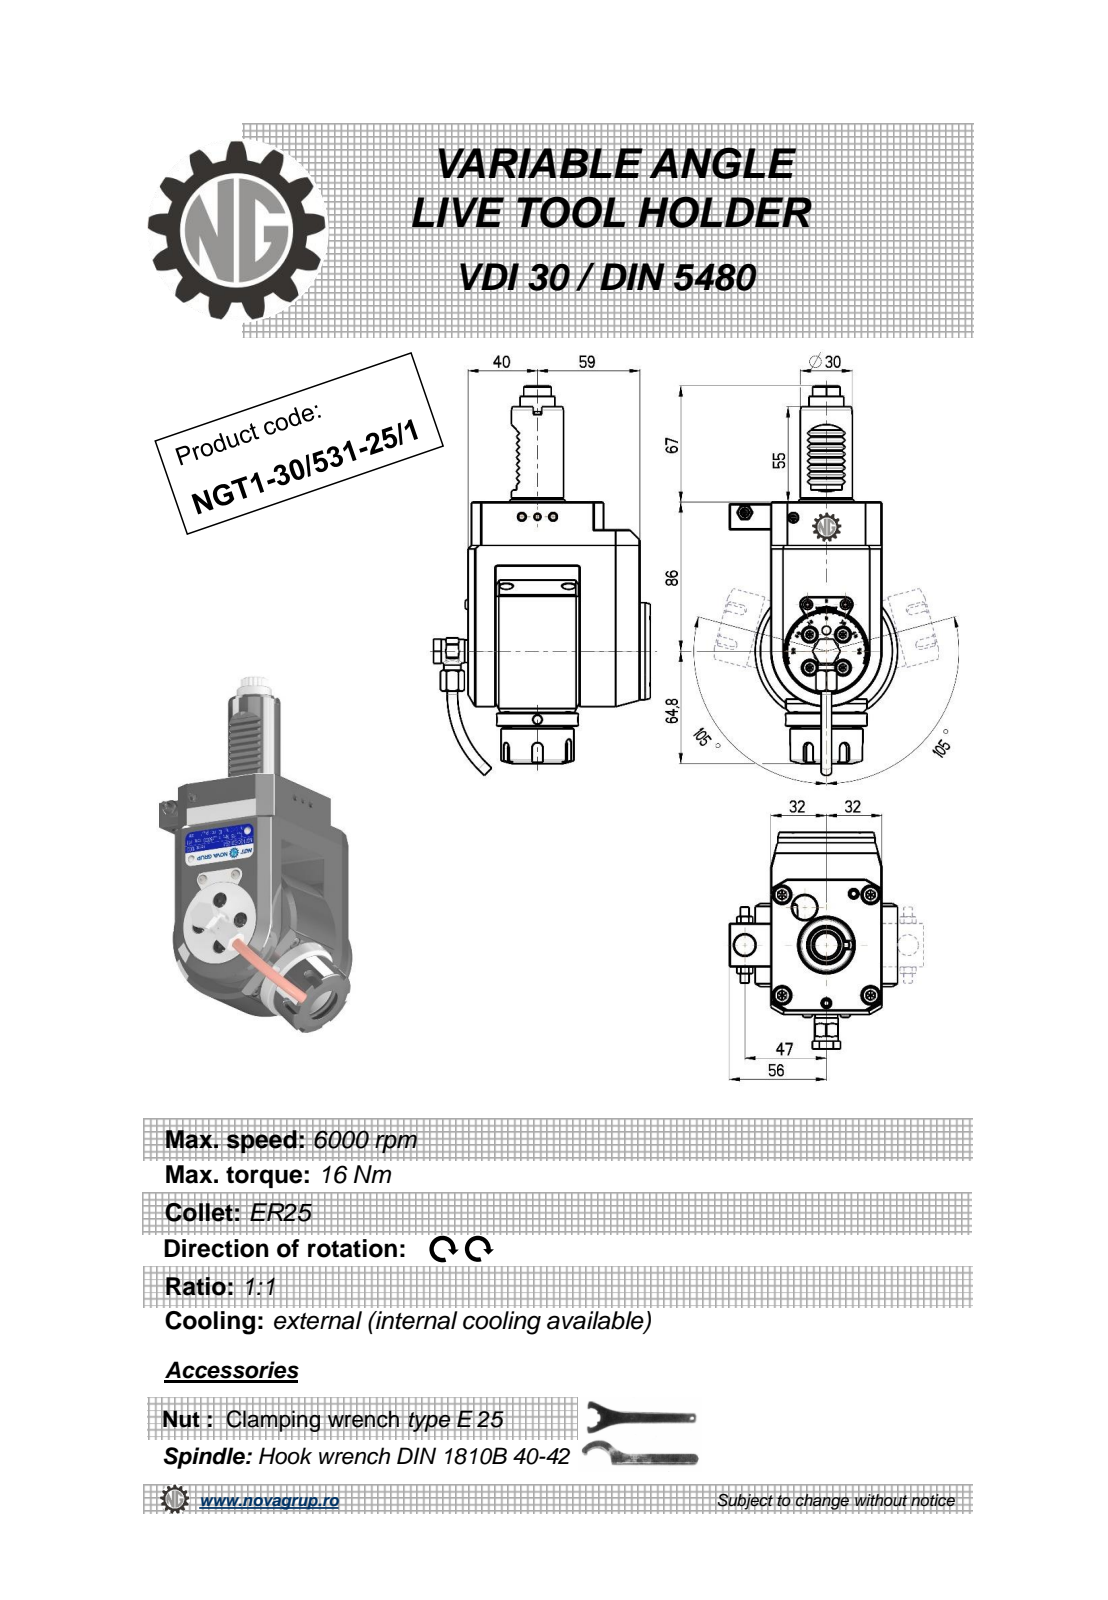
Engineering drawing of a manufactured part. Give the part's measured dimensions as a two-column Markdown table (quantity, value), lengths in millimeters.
| quantity | value |
| --- | --- |
| part name | NGT1_30_531_25_1 |
| STEP written by | PRO/ENGINEER BY PARAMETRIC TECHNOLOGY CORPORATION, 2010280 (CONFIG_CONTROL_DESIGN) |
| units | millimeters |
| bodies | 1 solid, 643 faces (233 planar, 207 cylindrical, 203 other) |
| overall size | 224.67 × 124.9 × 97 |
| volume | 790 116 mm³ |
| surface area | 76 472 mm² |
| round holes (diameter × count) | 4 × 3, 5 × 2, 3 × 1, 4.2 × 1, 6.2 × 1, 9 × 1, 9.5 × 1, 11 × 1, 12 × 1, 20.3 × 1 |
| round bosses / shafts (diameter × count) | 10 × 2, 6 × 2, 5.7 × 2, 82 × 1, 56 × 1, 47 × 1, 42 × 1, 35 × 1 |
| partial cylindrical surfaces (radius × count) | 1.98 × 36, 0.26 × 12, 0.3 × 8, 0.16 × 6, 3 × 5, 0.5 × 4, 1 × 2, 7.29 × 1 |
| main face-to-face distances | 64, 16, 37, 6, 99, 105, 21, 14, 83, 35 |
| hole center spacings | 0.4, 39.45, 47, 49, 49.4, 67.9, 68.19, 92.78 |
